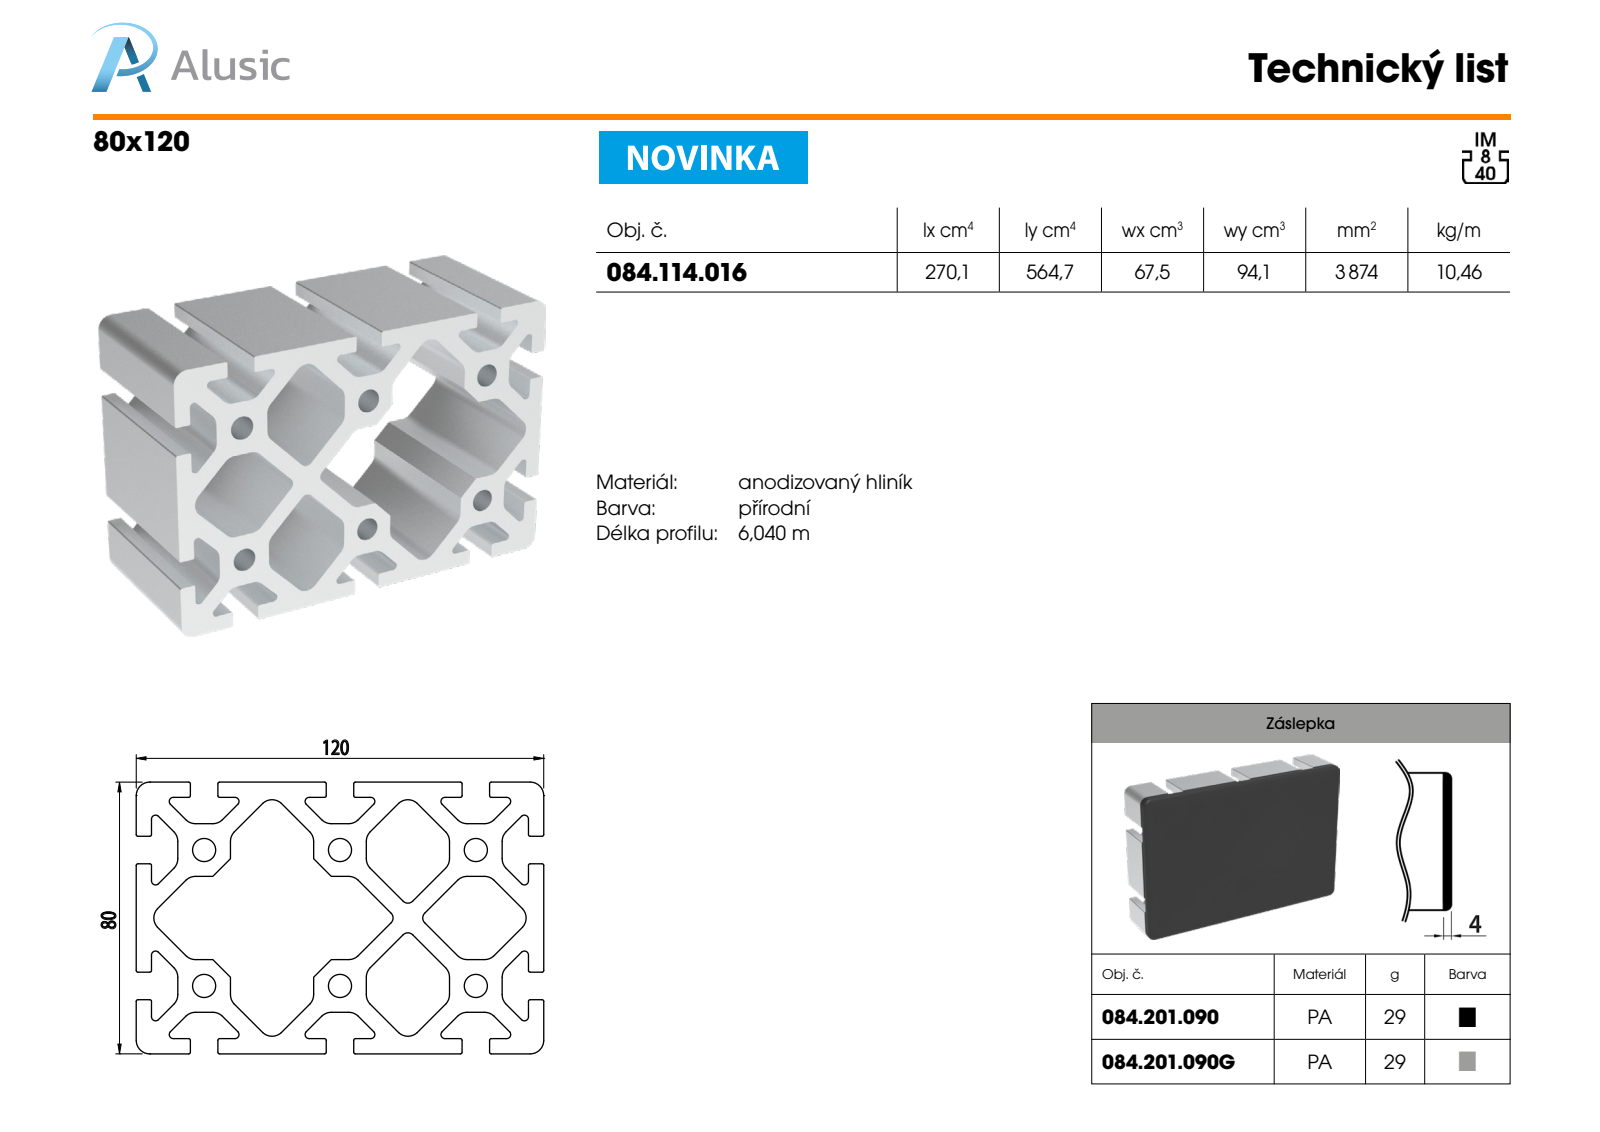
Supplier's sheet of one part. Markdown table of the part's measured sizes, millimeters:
| quantity | value |
| --- | --- |
| part name | 084.114.016 |
| STEP written by | SolidWorks 2018 (AUTOMOTIVE_DESIGN) |
| units | millimeters |
| bodies | 1 solid, 257 faces (124 planar, 133 cylindrical, 0 other) |
| overall size | 120 × 100 × 80 |
| volume | 387 403 mm³ |
| surface area | 146 184 mm² |
| round holes (diameter × count) | 6.8 × 6 |
| partial cylindrical surfaces (radius × count) | 4 × 50, 0.5 × 40, 1.2 × 20, 2 × 4 |
| main face-to-face distances | 28.28, 5, 56.56, 80, 40, 23.28, 4.5, 51.56, 33.28, 3.7 |
| hole center spacings | 40, 56.57, 80, 89.44 |
